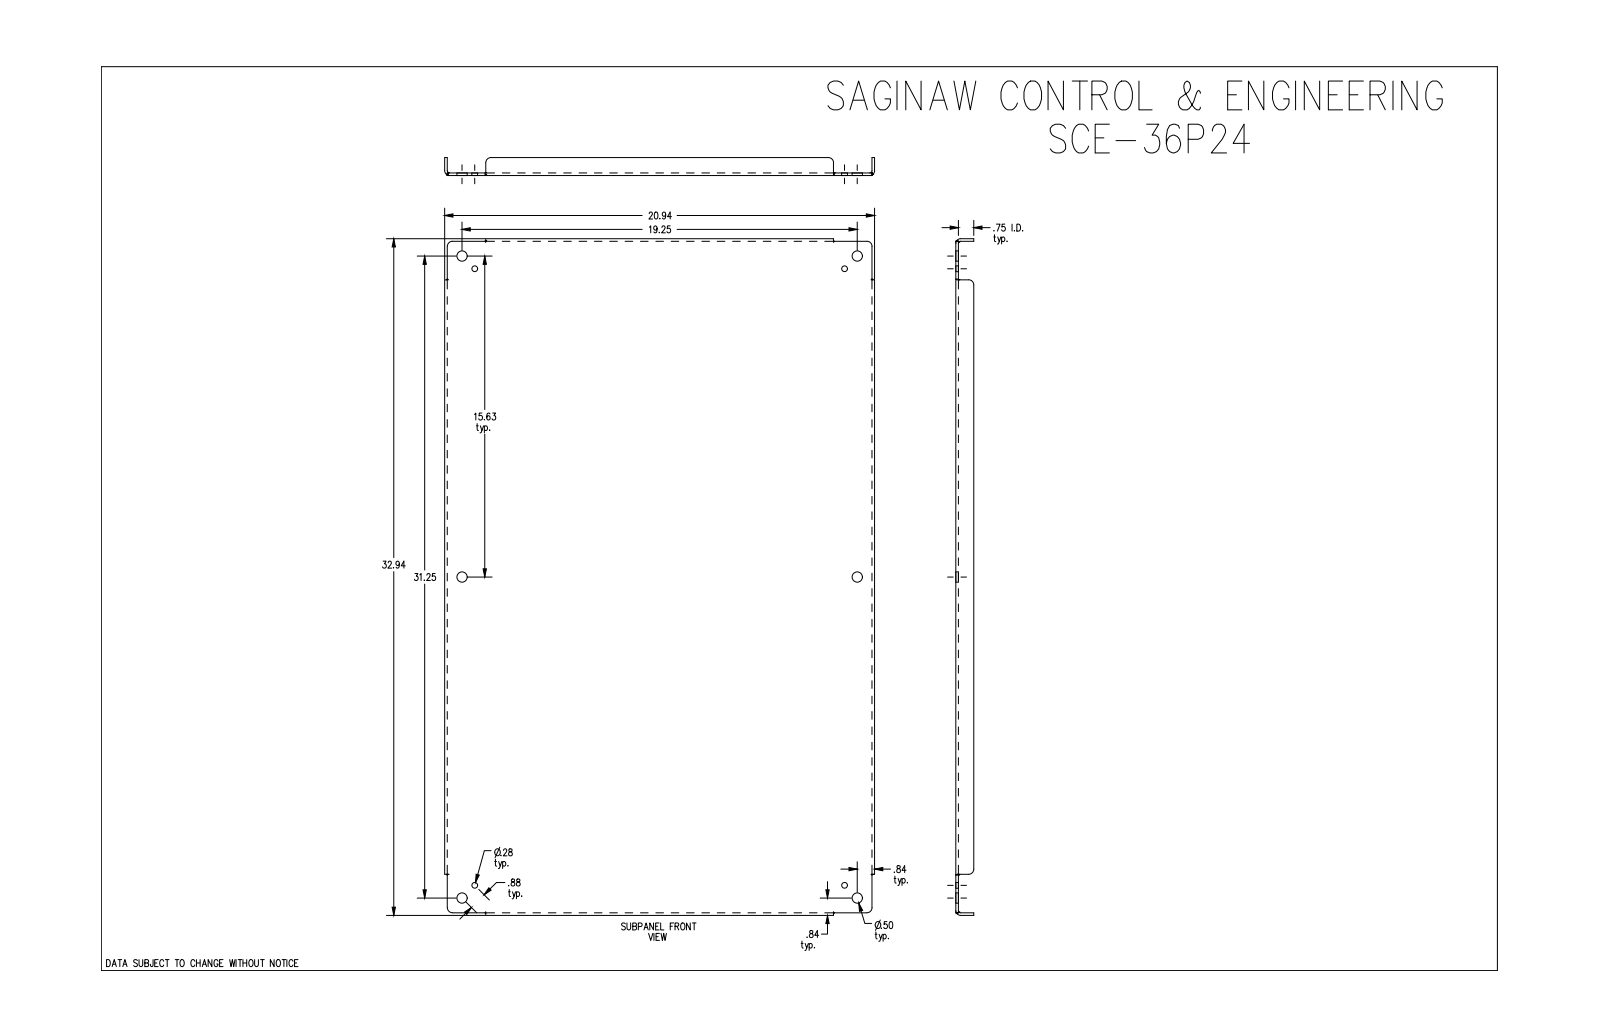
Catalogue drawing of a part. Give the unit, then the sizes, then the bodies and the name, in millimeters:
Units: millimetres
Overall size (bounding box): 836.6 × 531.8 × 22.2
Round holes (diameter × count): ⌀12.7 ×6, ⌀7.1 ×4
Partial cylindrical surfaces — rounded edges, fillets, slot ends (radius × count): R6.4 ×8, R2.8 ×4, R6 ×4
Main face-to-face distances: 3.2, 3.2, 528.7, 833.5, 525.4, 531.8, 19.1, 22.2, 830.2, 836.6
Hole centre spacings: 22.2, 381.5, 396.9, 473.5, 607.6, 629.7, 778.2, 910.7
Volume: 1 532 000 mm³ · Surface area: 975 500 mm²
Bodies: 1 solid, 84 faces (30 planar, 30 cylindrical, 24 other)
Part name (STEP PRODUCT): SCE-36P24
STEP written by: SolidWorks 2019 (CONFIG_CONTROL_DESIGN)
